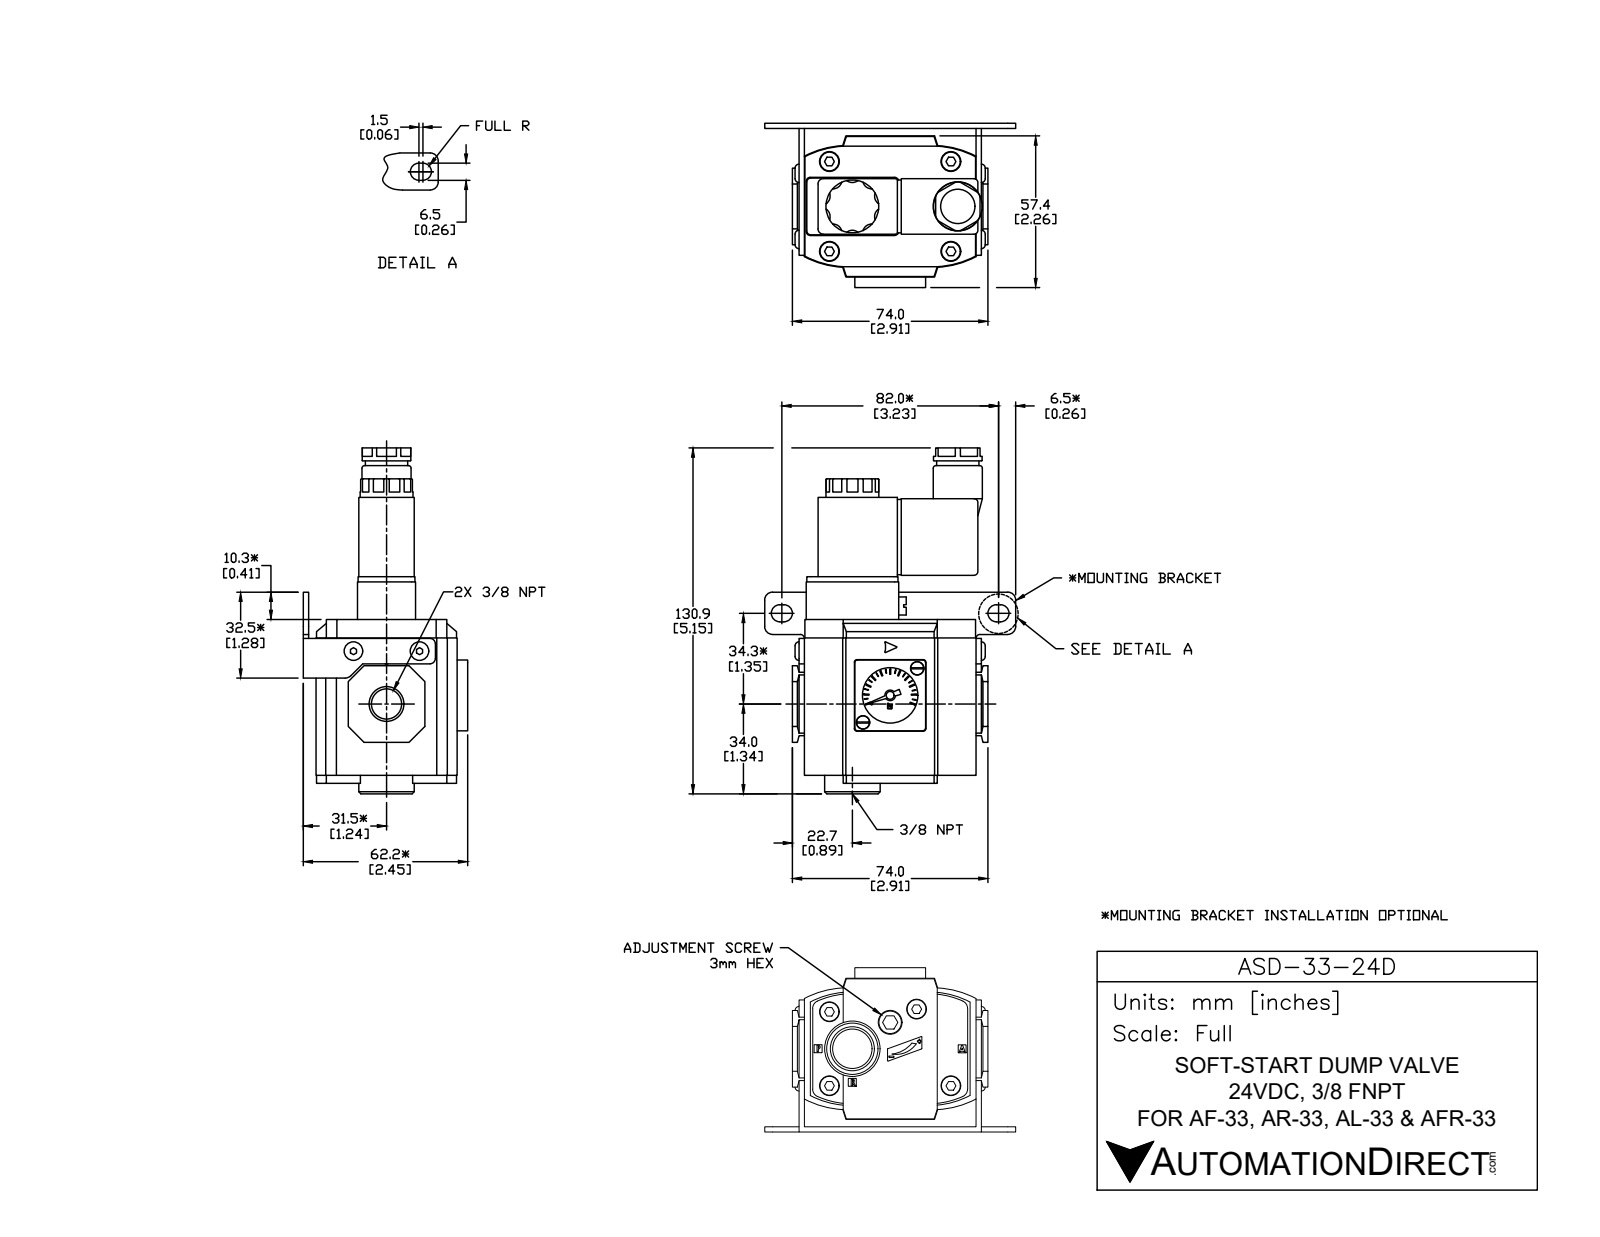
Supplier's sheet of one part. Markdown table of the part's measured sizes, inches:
| quantity | value |
| --- | --- |
| part name | ASD-33-24D |
| STEP written by | SolidWorks 2015 (CONFIG_CONTROL_DESIGN) |
| units | inches |
| bodies | 22 solids, 550 faces (343 planar, 164 cylindrical, 43 other) |
| overall size | 5.154 × 3.74 × 2.476 |
| volume | 15.49 in³ |
| surface area | 94.46 in² |
| round holes (diameter × count) | 0.157 × 8, 0.295 × 8, 0.118 × 2, 0.827 × 2, 0.335 × 1, 0.354 × 1, 0.512 × 1, 0.562 × 1, 0.589 × 1 |
| round bosses / shafts (diameter × count) | 0.28 × 8, 0.098 × 2, 0.787 × 1, 0.732 × 1, 0.724 × 1, 0.63 × 1, 0.157 × 1 |
| partial cylindrical surfaces (radius × count) | 0.059 × 10, 0.124 × 10, 0.039 × 6, 0.118 × 6, 0.029 × 4, 0.049 × 4, 0.128 × 4, 1.37 × 4 |
| main face-to-face distances | 0.118, 0.079, 2.047, 2.323, 0.276, 0.827, 0.52, 1.346, 0.638, 1.465 |
| hole center spacings | 0.118, 1.22, 1.811, 1.815, 2.184, 0.571, 0.649, 0.677 |
